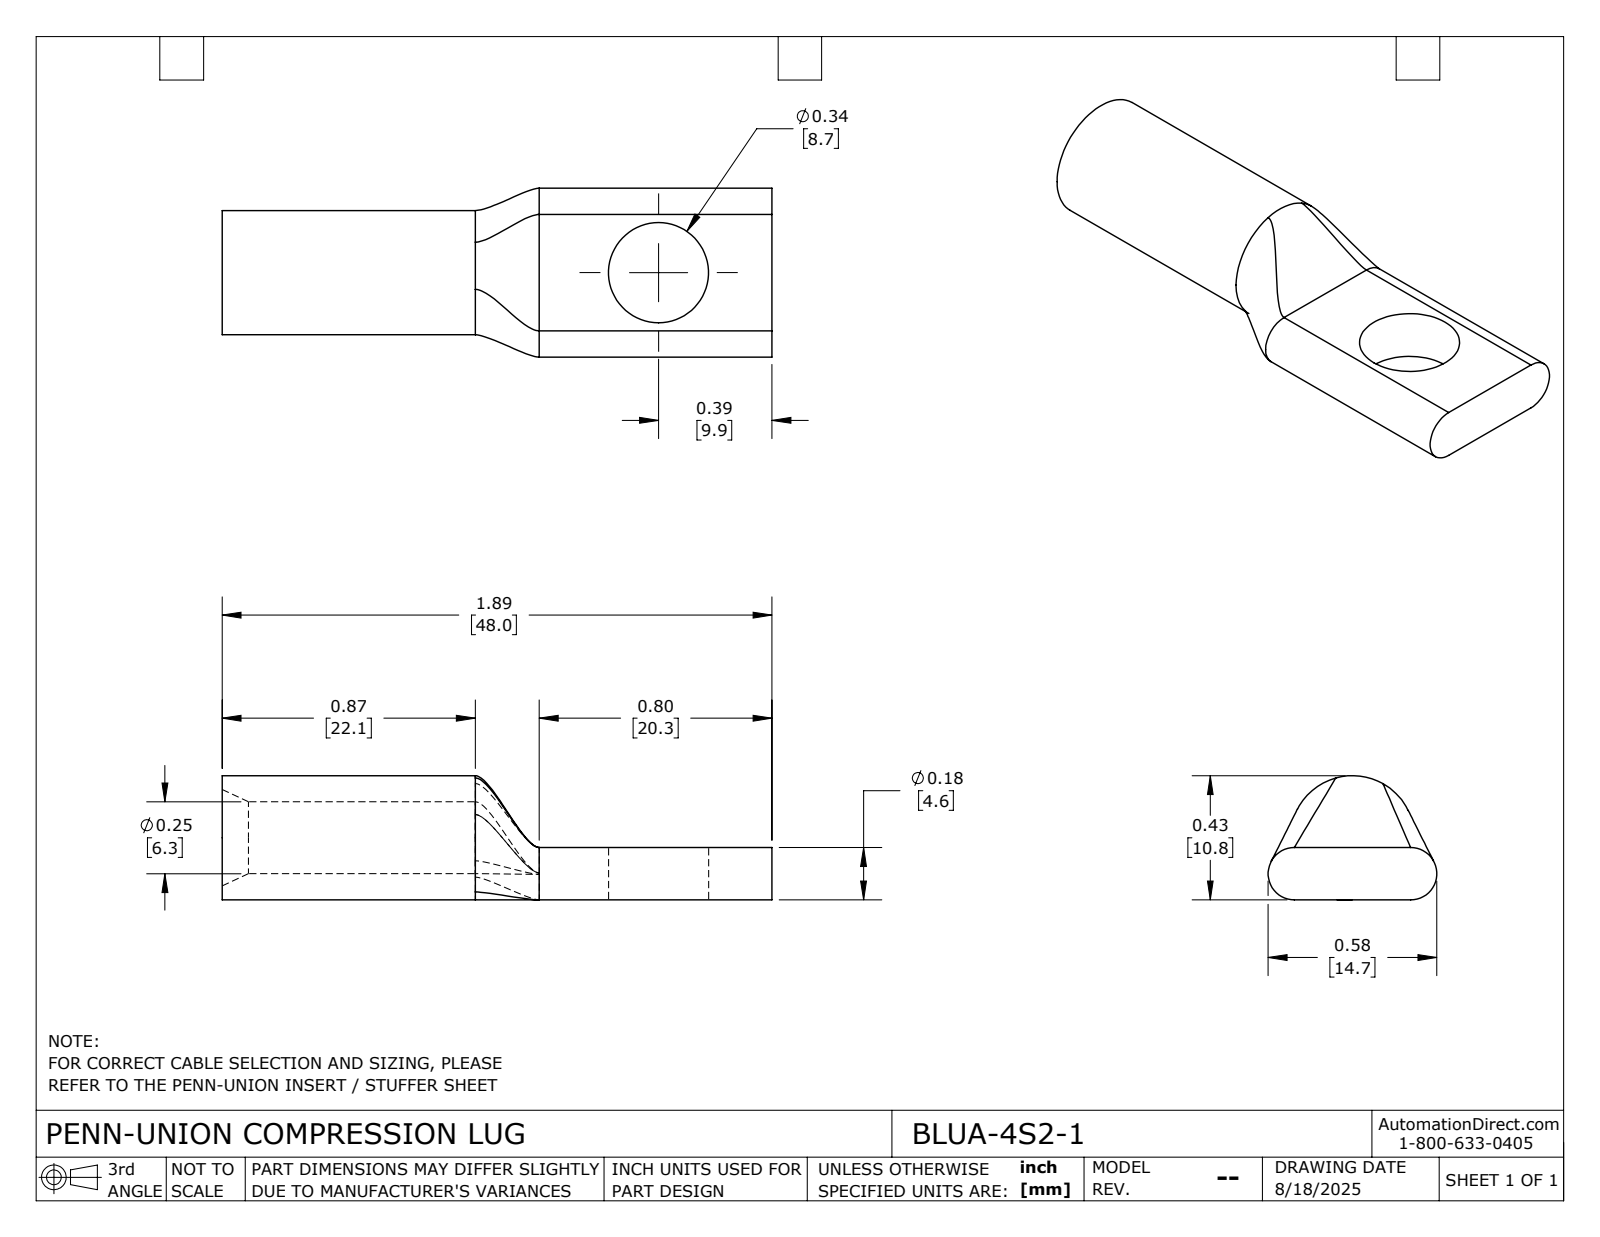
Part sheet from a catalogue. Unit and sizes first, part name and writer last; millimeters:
Units: millimetres
Overall size (bounding box): 48 × 14.7 × 10.8
Round holes (diameter × count): ⌀6.3 ×1, ⌀8.7 ×1
Round bosses / shafts (diameter × count): ⌀10.8 ×1
Partial cylindrical surfaces — rounded edges, fillets, slot ends (radius × count): R2.3 ×2
Main face-to-face distances: 4.6, 48, 27.7, 20.3
Volume: 2 670 mm³ · Surface area: 2 366 mm²
Bodies: 1 solid, 24 faces (5 planar, 9 cylindrical, 10 other)
Part name (STEP PRODUCT): BLUA-4S2-1
STEP written by: SolidWorks 2024 (CONFIG_CONTROL_DESIGN)
